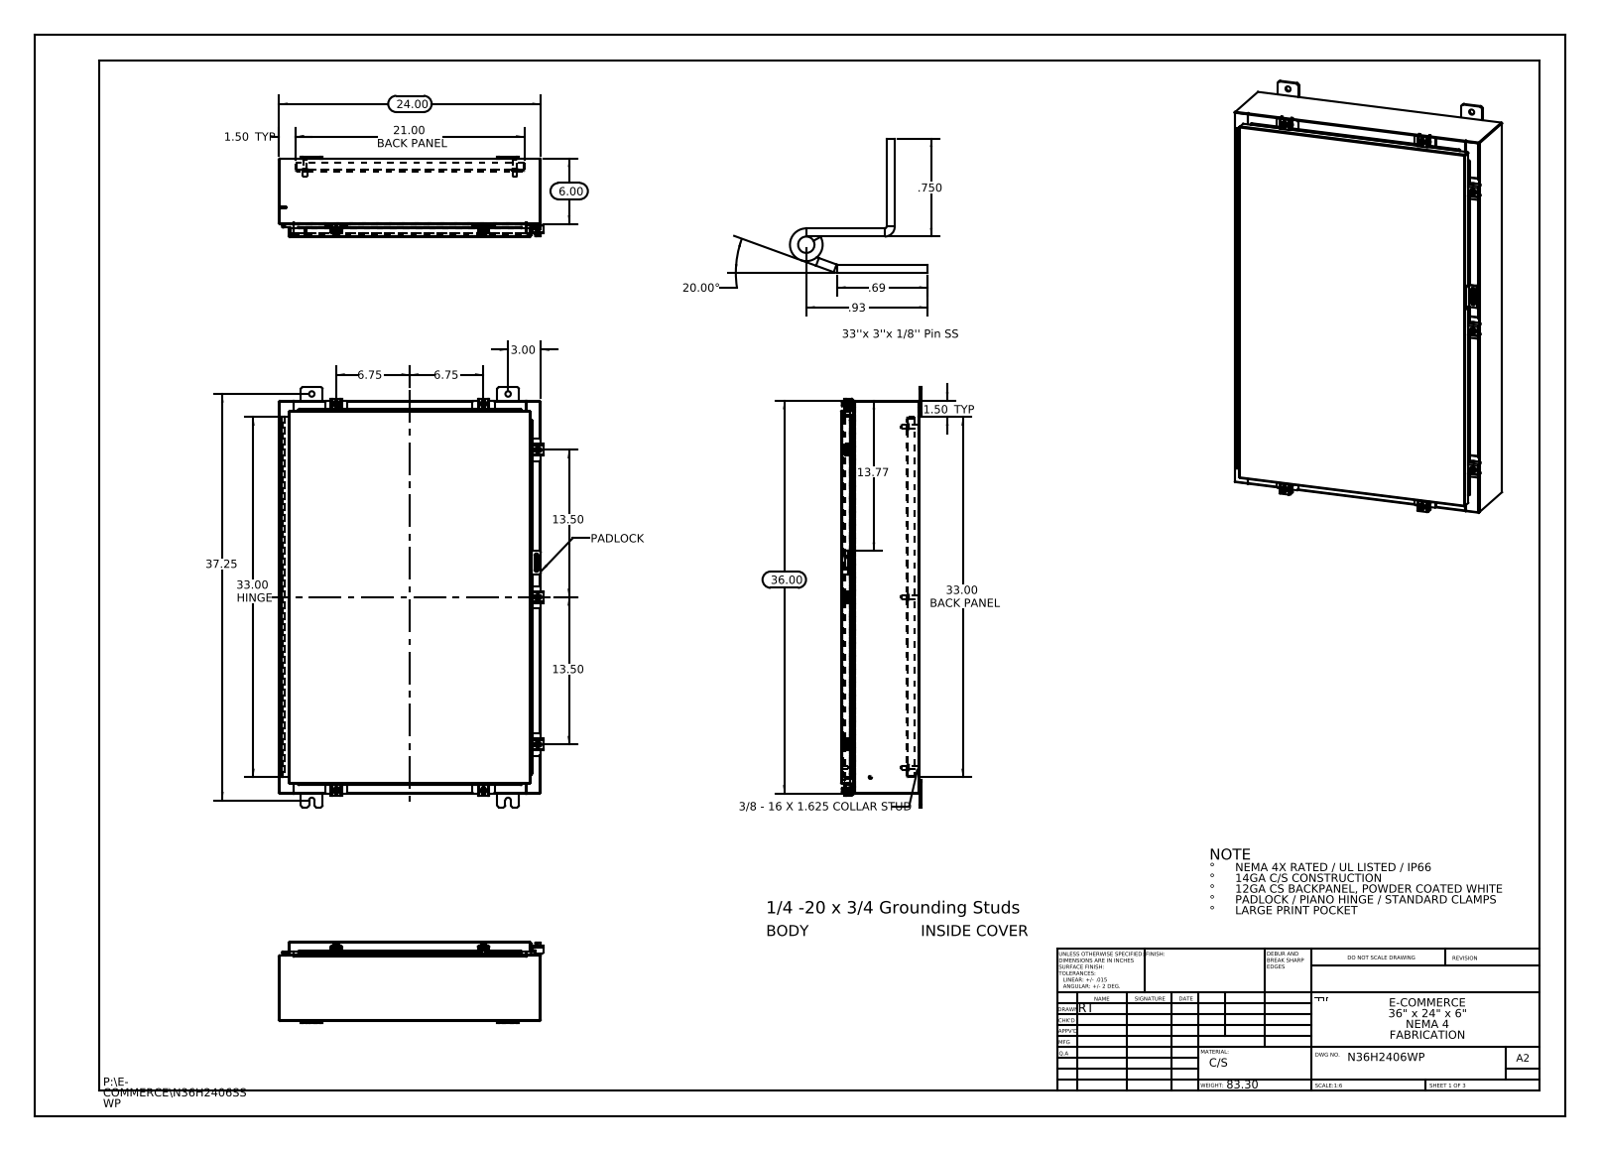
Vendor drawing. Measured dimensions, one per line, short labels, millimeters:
name: N36H2406SSWP Padlock Hasp; N36H2406WP; N36H2406SSWP Padlock Staple; Quarter-20 CD Stud (+8 more)
written by: SolidWorks 2013 (CONFIG_CONTROL_DESIGN)
unit: mm
bodies: 56 solids, 2210 faces (1144 planar, 930 cylindrical, 136 other)
size: 977.9 × 615 × 187.7
volume: 4 798 000 mm³; area: 4 690 000 mm²
holes: 10× ⌀12.7, 7× ⌀5.4, 7× ⌀6.6, 2× ⌀3.2, 1× ⌀3.2
bosses: 8× ⌀6.4, 7× ⌀12.7, 7× ⌀10.1, 6× ⌀15.9, 6× ⌀9.5, 6× ⌀8.4, 2× ⌀8, 2× ⌀6
rounds: 34× R1.5, 27× R0.3, 24× R4.8, 21× R2.2, 14× R3, 14× R3.6, 11× R1.3, 10× R2
face distances: 1.9, 181, 179.1, 182.9, 2.6, 25.4, 27.3, 153.7, 155.6, 29.9
hole spacings: 342.9, 396.9, 456.1, 629.7, 850.2, 943.7, 489, 47.2
